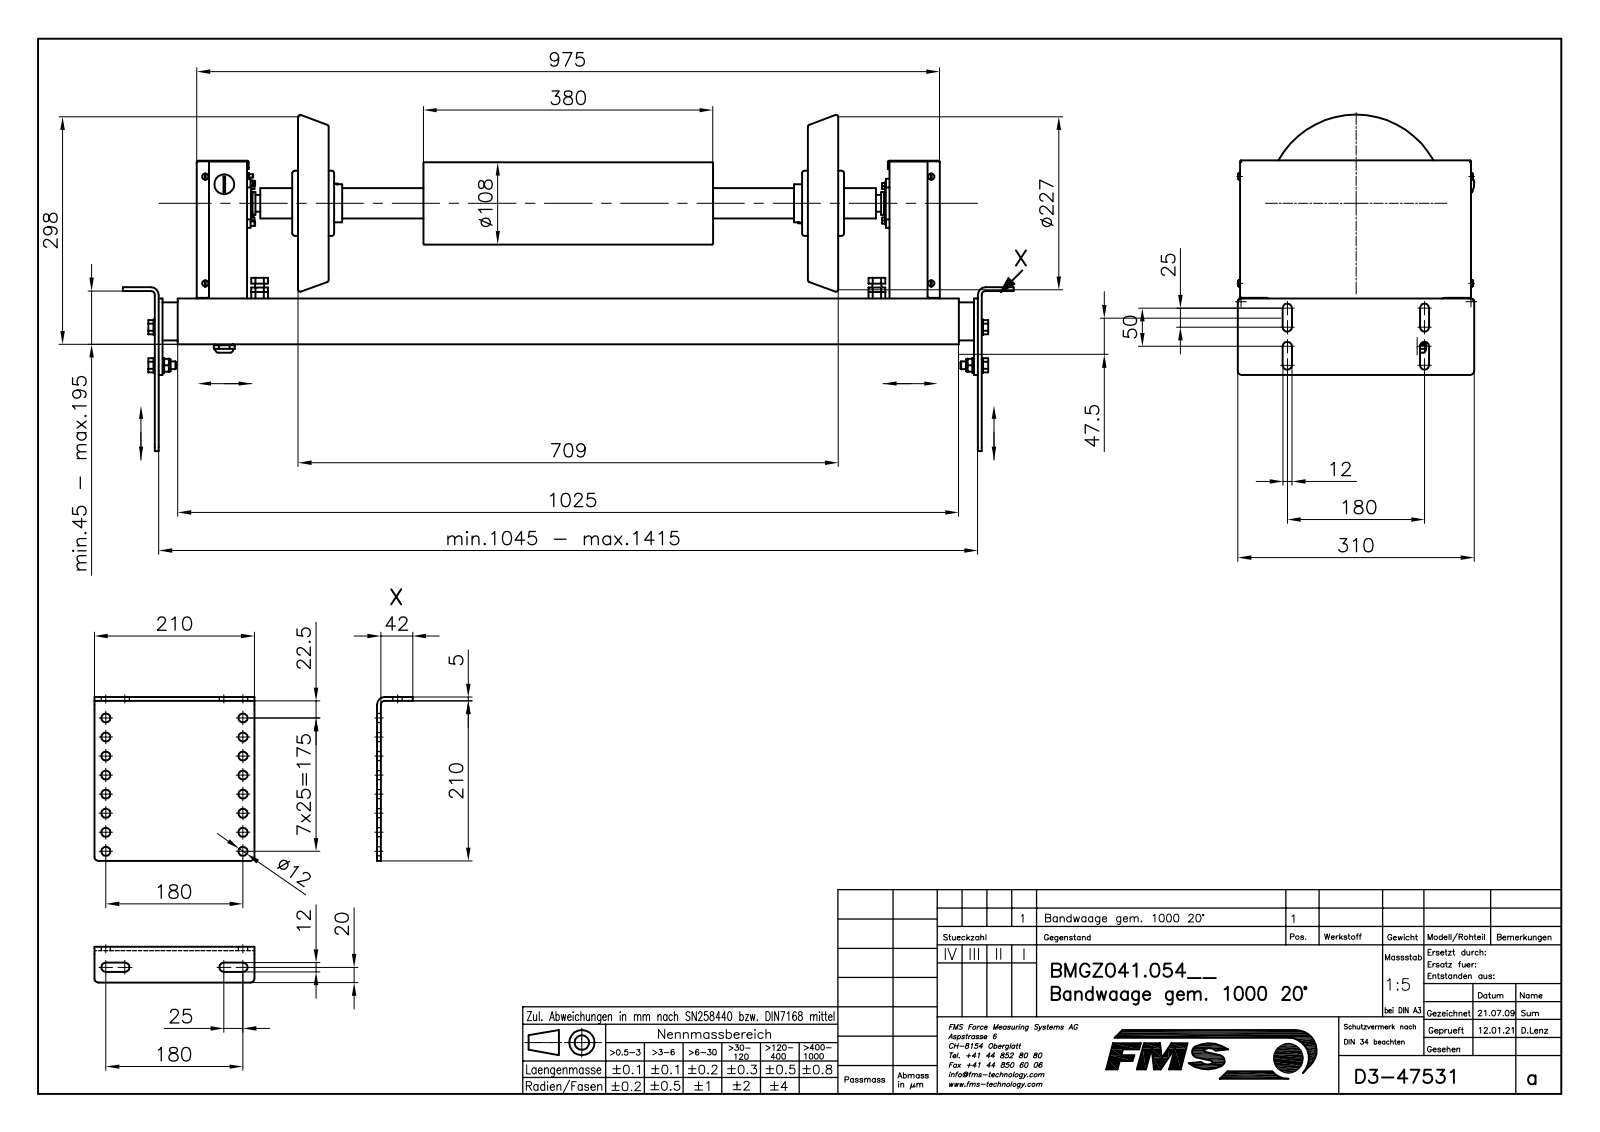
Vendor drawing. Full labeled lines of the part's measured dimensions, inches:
Part name (STEP PRODUCT): B47531_STP; B50108; 6KT-SCHRAUBE_M12X30; ZYL_SCHR__M4X8 (+8 more)
STEP written by: Mechanical Desktop 2009 (CONFIG_CONTROL_DESIGN)
Units: inches
Bodies: 159 solids, 2692 faces (1359 planar, 954 cylindrical, 379 other)
Overall size (bounding box): 46.024 × 17.362 × 12.213
Volume: 409.1 in³ · Surface area: 5 143 in²
Round holes (diameter × count): ⌀0.472 ×17, ⌀0.197 ×6, ⌀0.138 ×4, ⌀0.193 ×4, ⌀0.252 ×4, ⌀0.342 ×4, ⌀0.344 ×4, ⌀0.394 ×4, ⌀0.413 ×4, ⌀0.42 ×4, ⌀0.583 ×4, ⌀0.161 ×3
Round bosses / shafts (diameter × count): ⌀0.472 ×11, ⌀0.323 ×8, ⌀0.165 ×8, ⌀0.787 ×6, ⌀0.394 ×6, ⌀0.197 ×5, ⌀0.63 ×4, ⌀0.437 ×4
Partial cylindrical surfaces — rounded edges, fillets, slot ends (radius × count): R0.079 ×34, R0.039 ×24, R0.157 ×16, R0.197 ×16, R0.236 ×12, R0.138 ×8, R0.089 ×6, R0.02 ×4
Main face-to-face distances: 0.157, 0.197, 0.039, 2.008, 10.63, 1.417, 2.205, 0.118, 1.969, 2.598
Hole centre spacings: 0.984, 7.155, 1.969, 7.355, 2.953, 7.677, 3.937, 7.087
